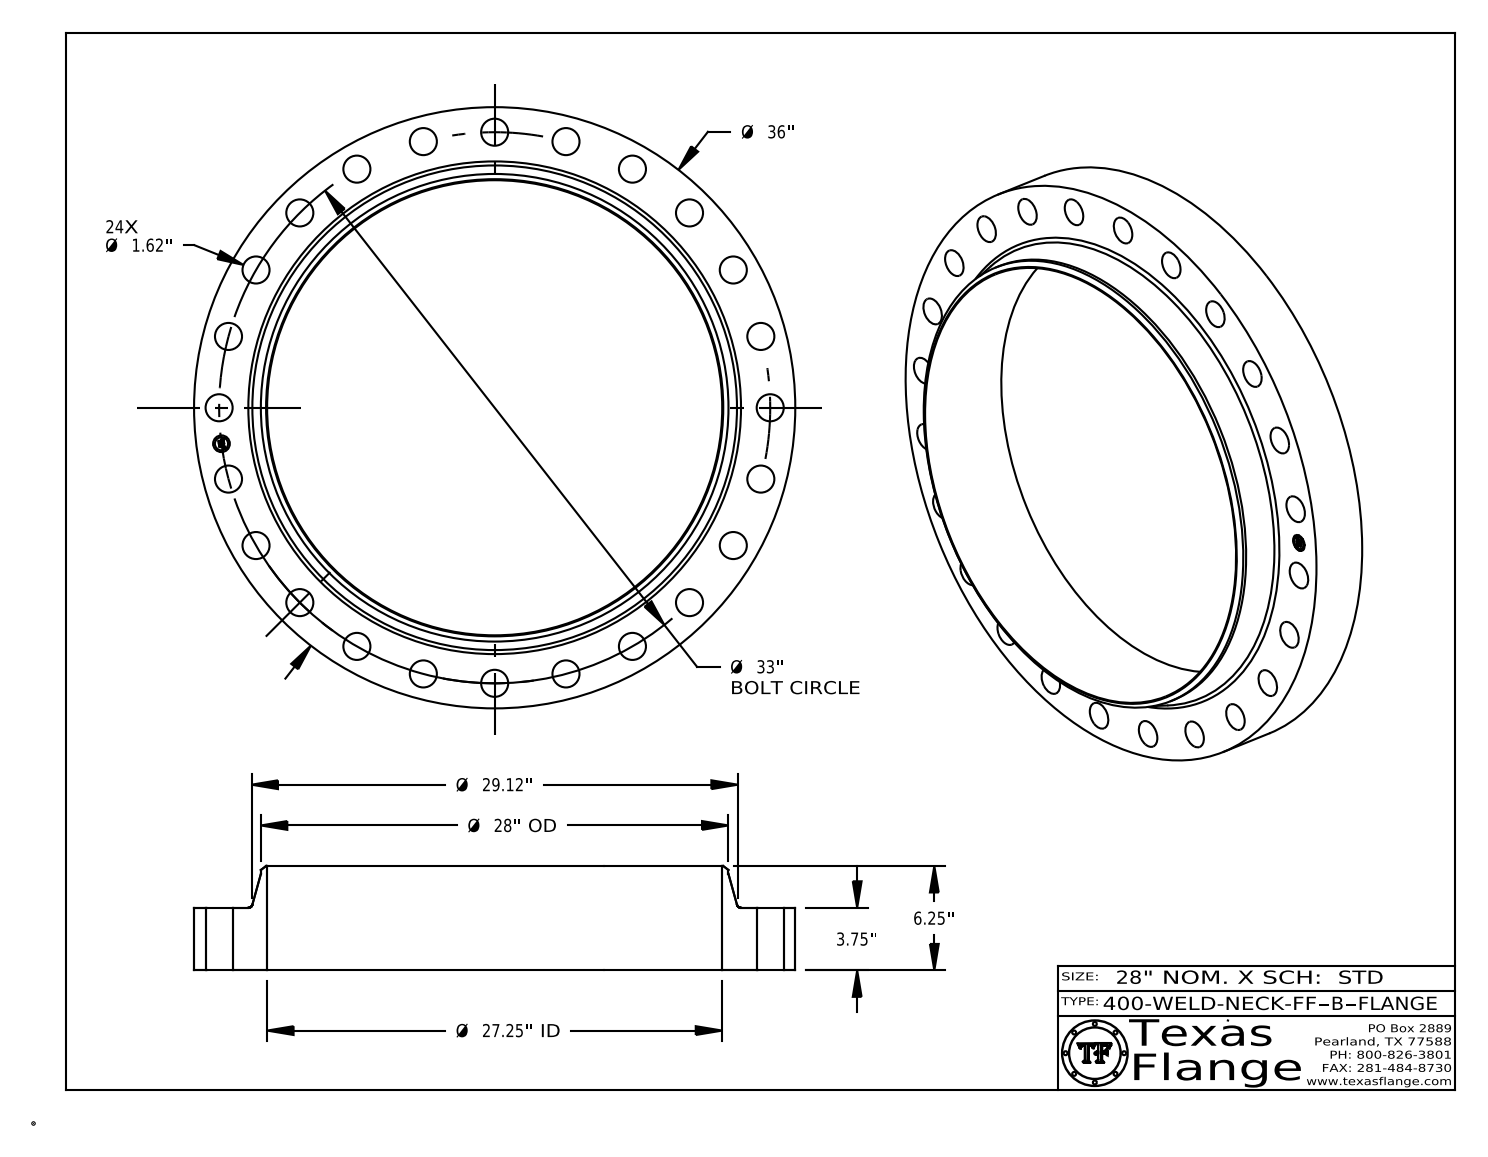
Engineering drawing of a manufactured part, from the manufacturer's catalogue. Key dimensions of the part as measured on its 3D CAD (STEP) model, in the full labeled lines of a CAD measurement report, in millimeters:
Part name (STEP PRODUCT): 400-WELD-NECK-FF, Series B
STEP written by: CATIA V5 STEP AP214 (AUTOMOTIVE_DESIGN)
Units: millimetres
Bodies: 1 solid, 448 faces (368 planar, 74 cylindrical, 6 other)
Overall size (bounding box): 914.4 × 914.4 × 158.8
Volume: 25 790 000 mm³ · Surface area: 1 515 000 mm²
Round holes (diameter × count): ⌀41.1 ×24, ⌀25.4 ×1, ⌀692.2 ×1
Round bosses / shafts (diameter × count): ⌀1.5 ×8, ⌀914.4 ×1, ⌀711.2 ×1, ⌀20 ×1
Main face-to-face distances: 95.3, 158.8, 63.5, 94.9, 0.4, 63.9, 7.6, 7.4, 1.4, 4.9
Hole centre spacings: 419.1, 109.4, 216.9, 510.3, 592.7, 665, 809.7, 831
